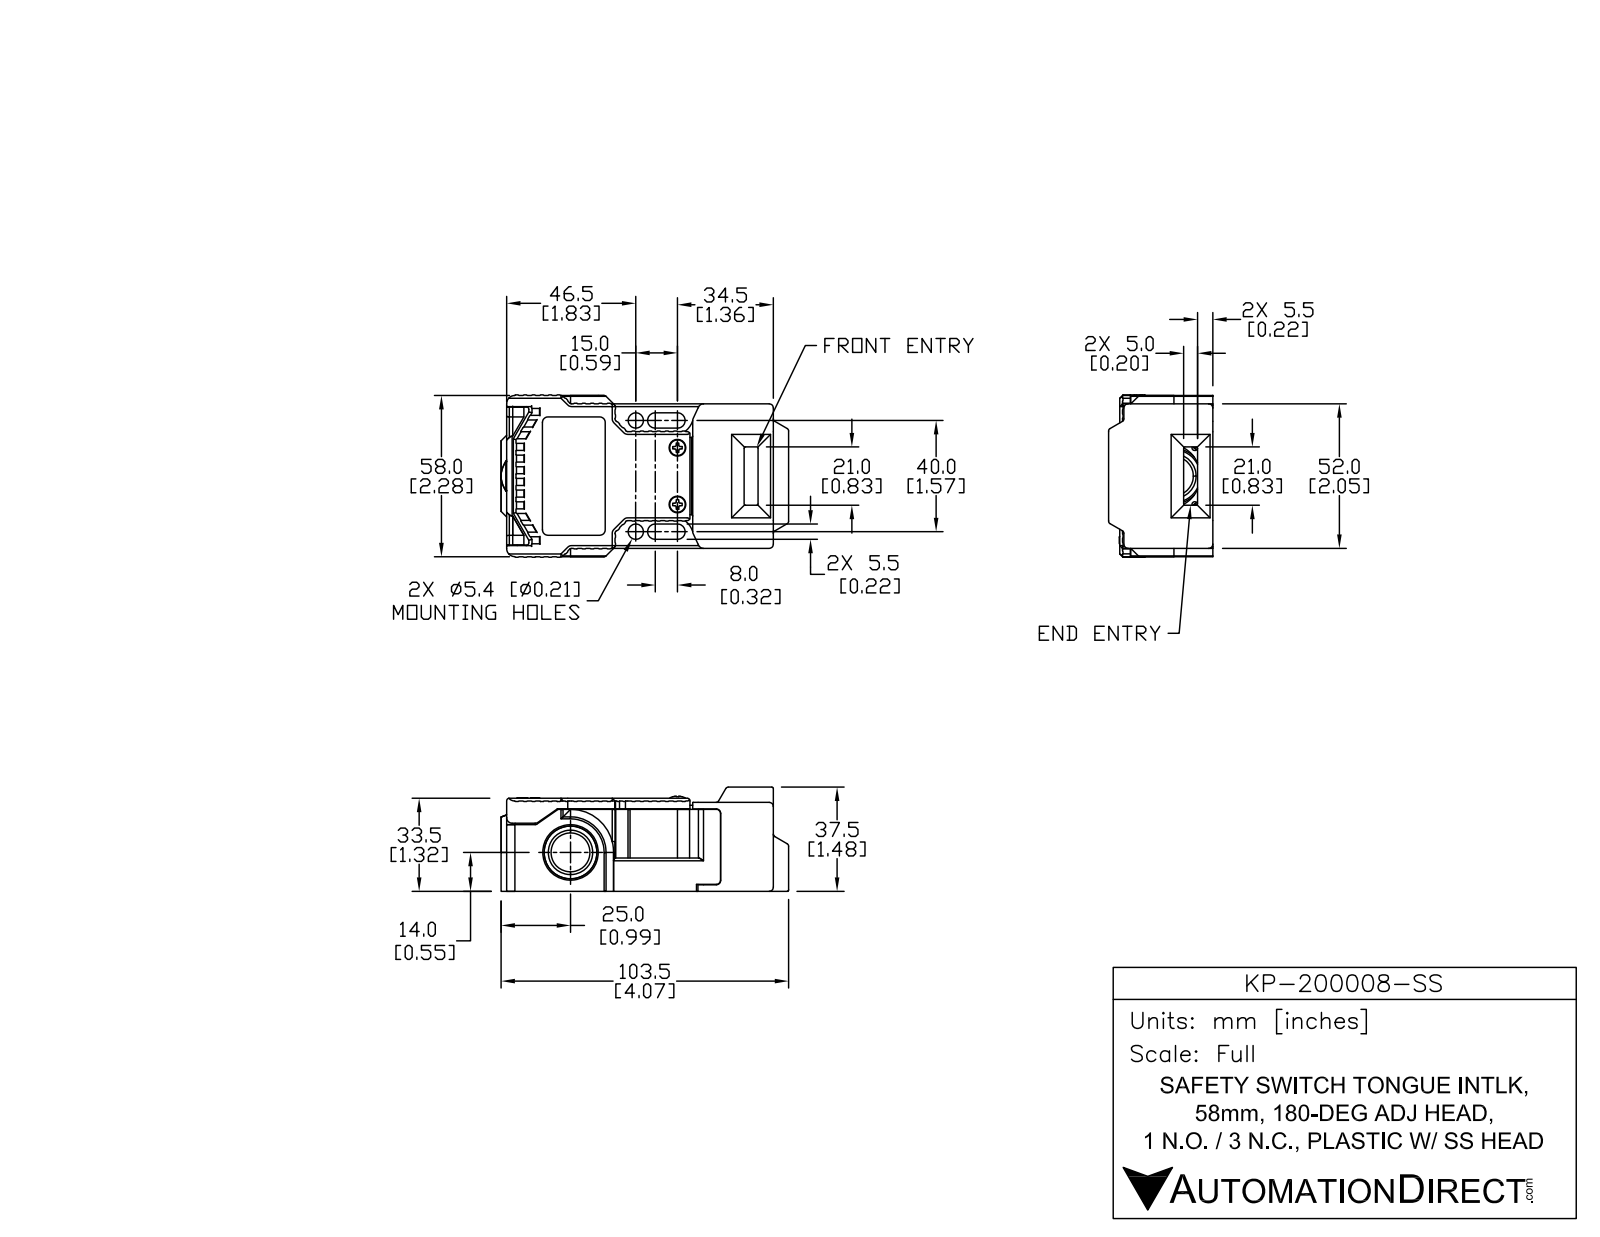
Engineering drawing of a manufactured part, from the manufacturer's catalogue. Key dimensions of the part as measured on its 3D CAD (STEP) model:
Part name (STEP PRODUCT): KP-200008-SS
STEP written by: SolidWorks 2013 (AUTOMOTIVE_DESIGN)
Units: millimetres
Bodies: 1 solid, 297 faces (177 planar, 81 cylindrical, 39 other)
Overall size (bounding box): 100.75 × 58 × 37.5
Volume: 157 757 mm³ · Surface area: 25 449 mm²
Round holes (diameter × count): ⌀5.4 ×2, ⌀19.33 ×1, ⌀20 ×1
Round bosses / shafts (diameter × count): ⌀5.6 ×2
Partial cylindrical surfaces — rounded edges, fillets, slot ends (radius × count): R1 ×36, R2 ×13, R2.75 ×4, R4 ×3, R2.25 ×2, R3 ×2, R3.25 ×2, R5 ×2
Main face-to-face distances: 33.5, 52, 3, 55, 33.45, 96, 1.05, 34.5, 1, 12.8
Hole centre spacings: 40
